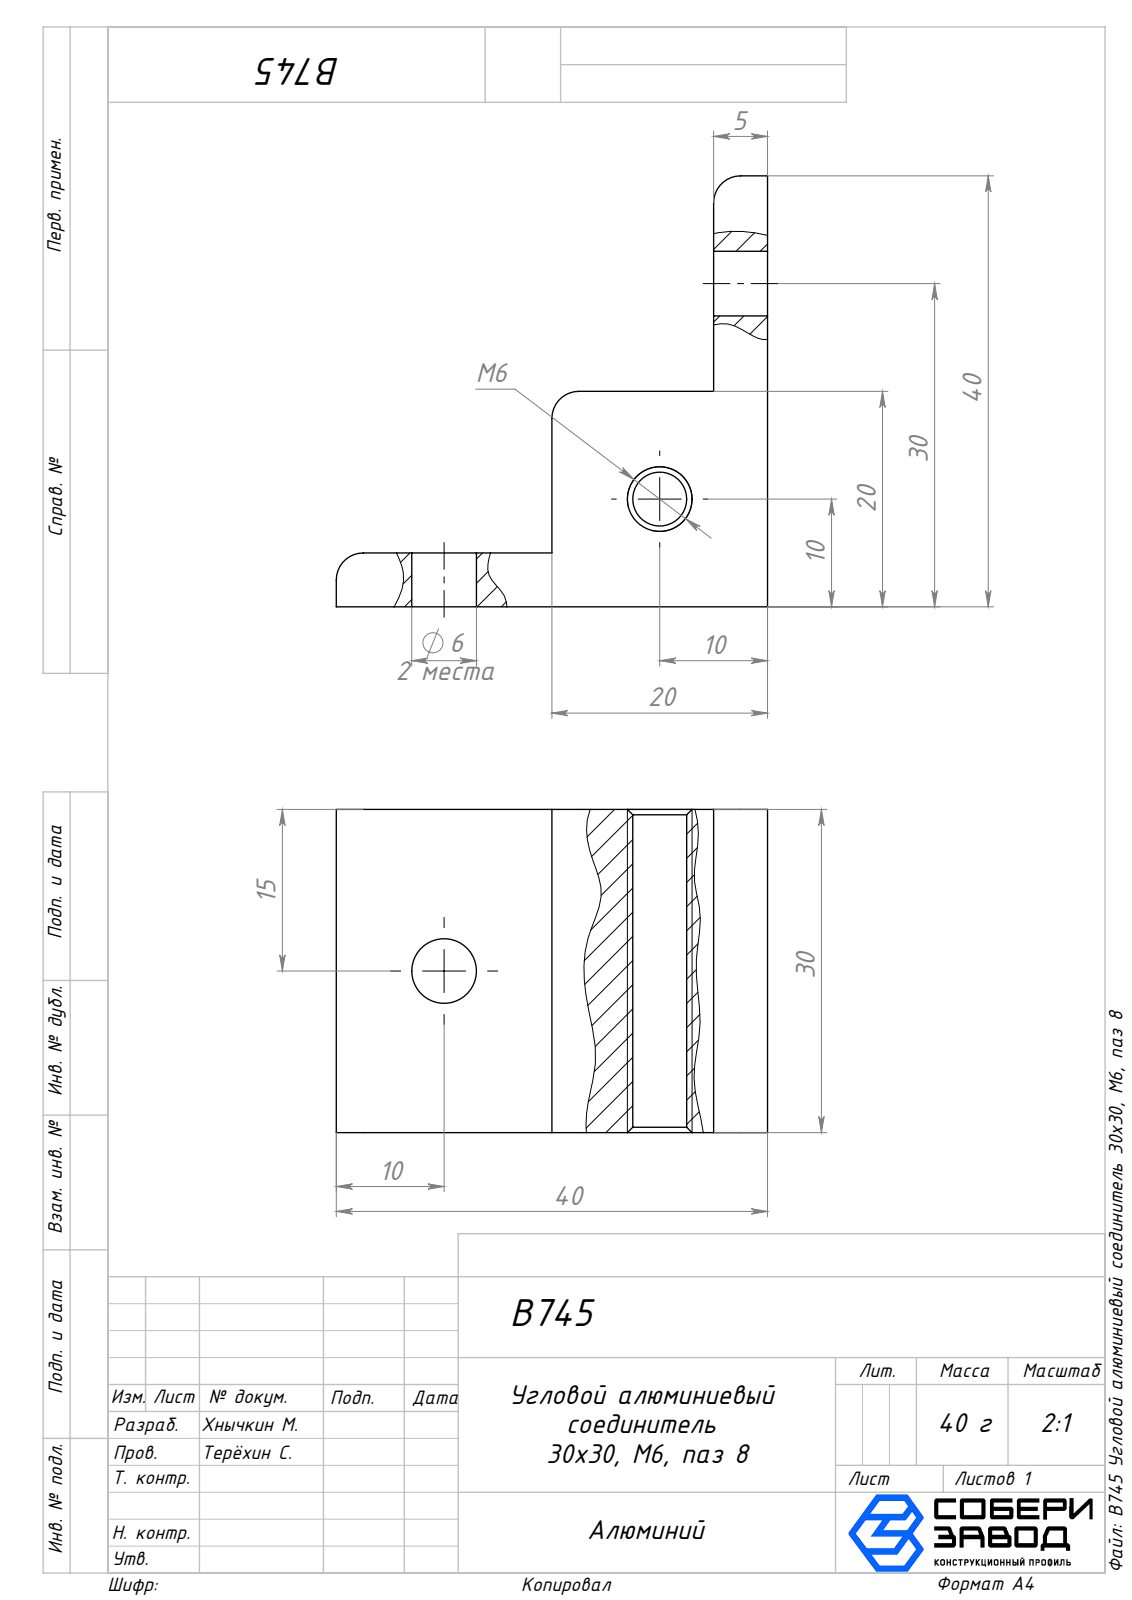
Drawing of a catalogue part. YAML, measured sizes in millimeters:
part_name: "B745 Угловой алюминиевый соединитель 30х30, M6, паз 8"
step_written_by: "SolidWorks 2025 (AUTOMOTIVE_DESIGN)"
units: millimeters
bodies: {solids: 1, faces: 23, planar: 10, cylindrical: 9, other: 4}
overall_size: [40, 40, 30]
volume: 17003
surface_area: 6394
round_holes:
  - {diameter: 6, count: 2}
  - {diameter: 5, count: 1}
partial_cylinders:
  - {radius: 2.5, count: 3}
face_to_face_distances: [5, 20, 15, 30, 40, 35]
